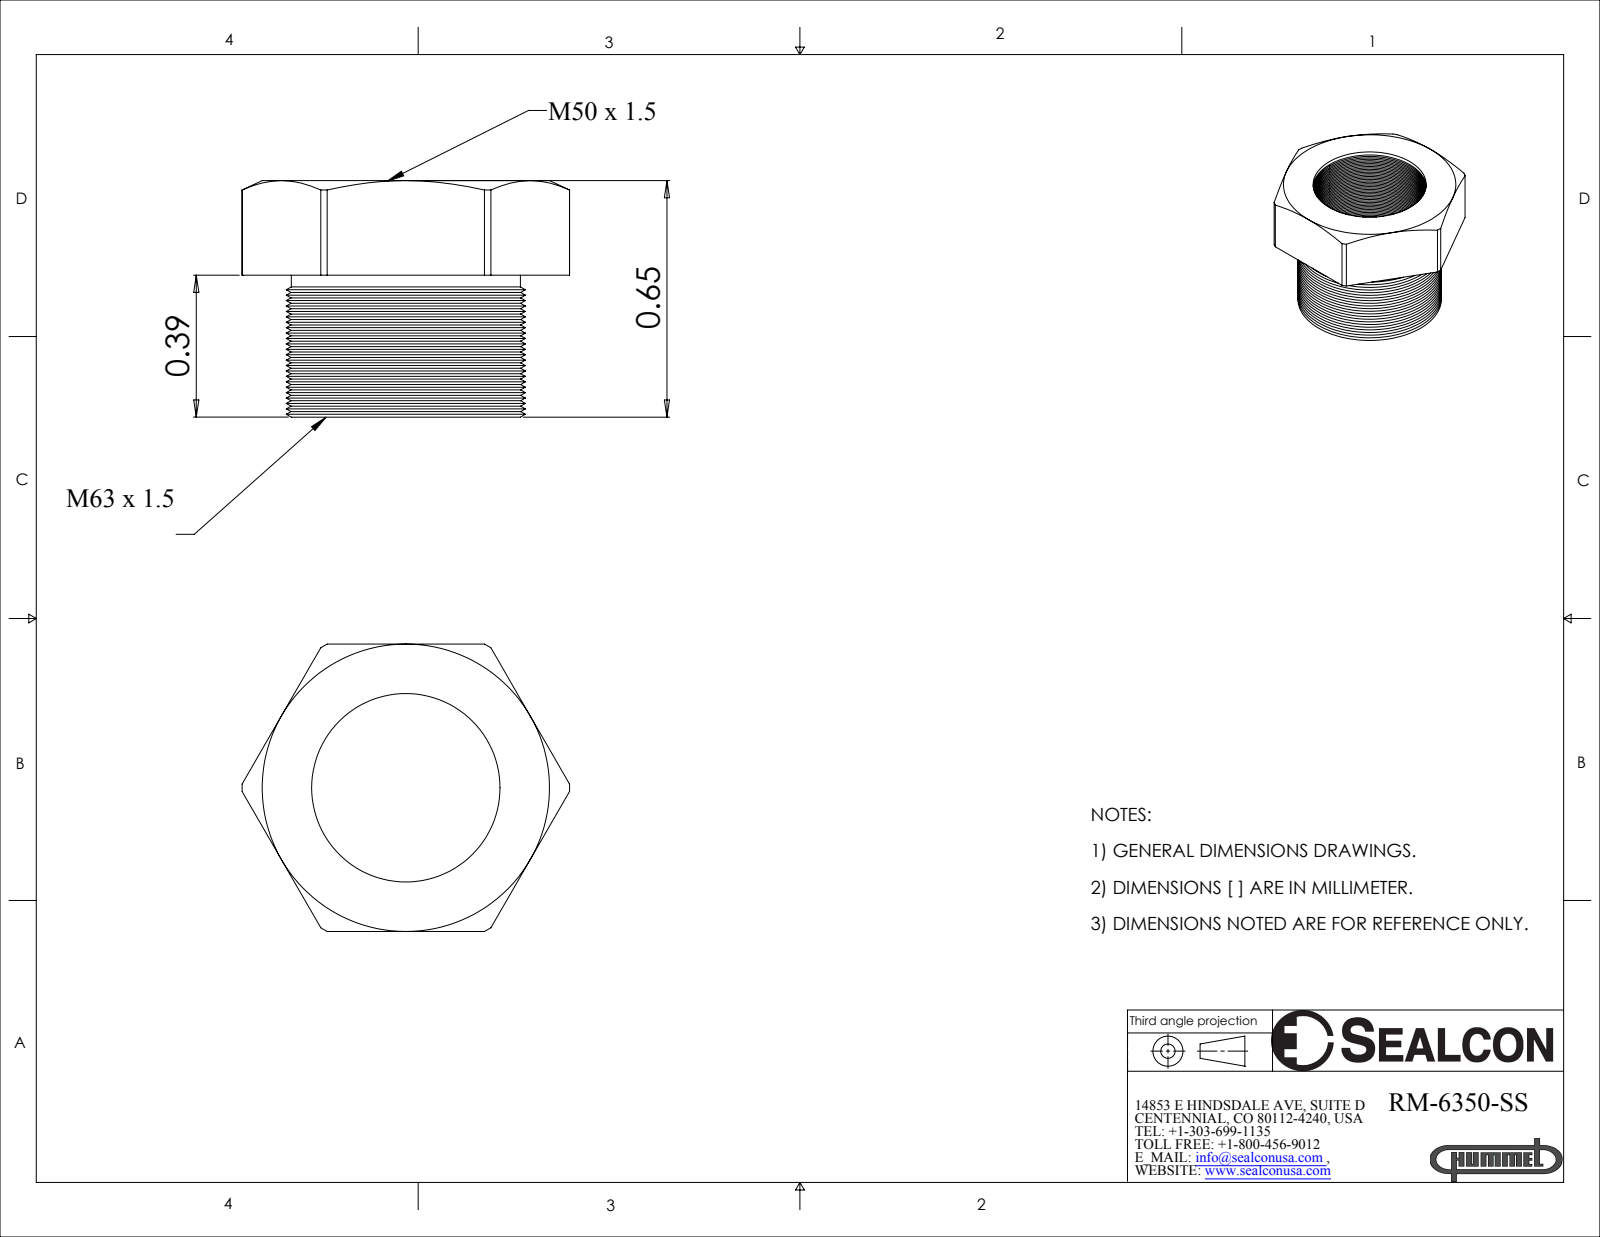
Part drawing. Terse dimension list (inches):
name: RM-6350-SS
written by: SolidWorks 2008 (CONFIG_CONTROL_DESIGN)
unit: in
bodies: 1 solid, 363 faces (9 planar, 91 cylindrical, 263 other)
size: 0.901 × 0.79 × 0.65
volume: 0.127 in³; area: 4.999 in²
holes: 1× ⌀0.518, 1× ⌀0.63
rounds: 1× R0.45
face distances: 0.79, 0.26, 0.39, 0.65
